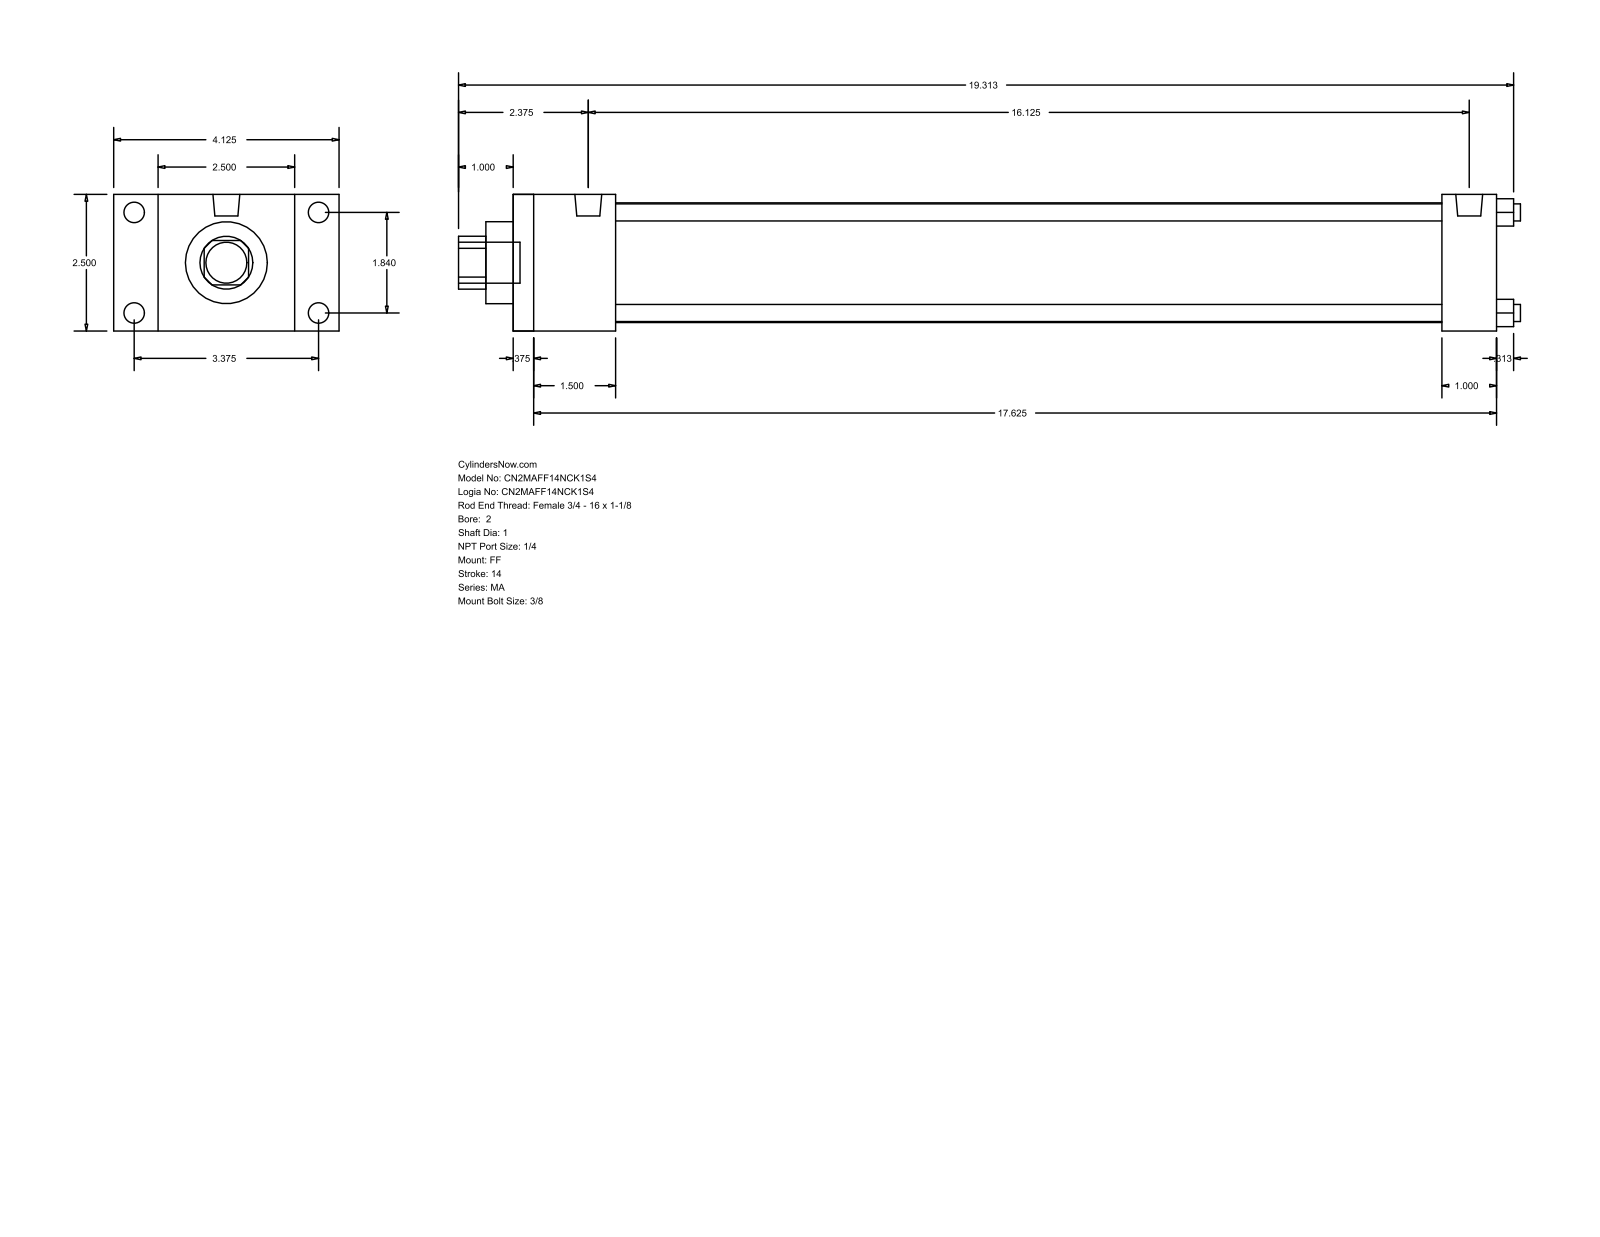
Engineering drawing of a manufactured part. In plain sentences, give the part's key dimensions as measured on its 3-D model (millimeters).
The part is named "MA_FF__0200_1". Its 3-D file was written by "GSSL Pune (CONFIG_CONTROL_DESIGN)". It is 0 solids with 92 faces: 64 planar, 28 cylindrical and 0 other. Overall it measures 493.71 by 104.78 by 63.5 millimeters. Round holes: 4 of diameter 7.94, 1 of diameter 25.4, 1 of diameter 38.1, 1 of diameter 55.63. Round bosses or shafts: 4 of diameter 9.53, 4 of diameter 7.94, 2 of diameter 12.49, 1 of diameter 19.05. Partial cylindrical surfaces (rounded edges, fillets, slot ends): 1 of radius 12.29. The main face-to-face distances are 63.5, 457.2, 9.52, 447.68, 25.4, 20.64, 12.7, 47.63, 431.8, 38.11. The hole center spacings are 33.05, 46.74, 66.1.
